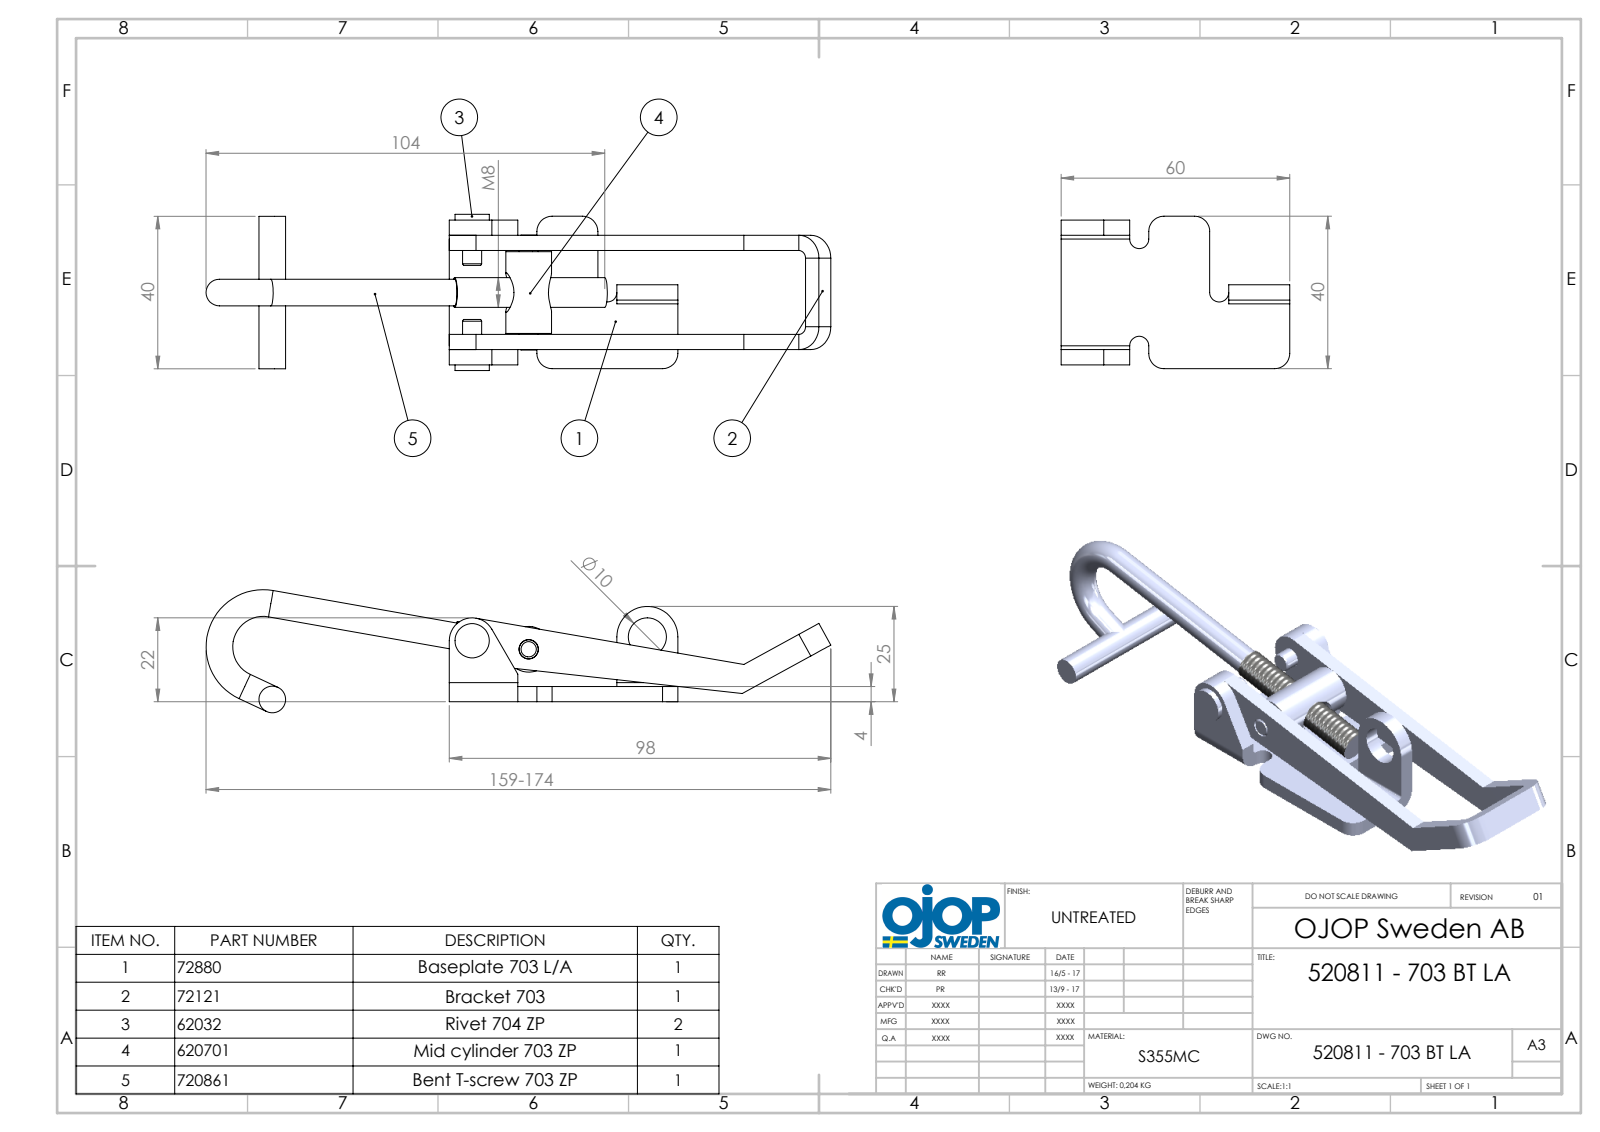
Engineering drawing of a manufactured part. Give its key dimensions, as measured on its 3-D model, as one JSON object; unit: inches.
{"part_name": "520811 - 703 BT LA; 704 - Rivet Gradin; 703- Platta LA; 703 - Rulle (+2 more)", "step_written_by": "SolidWorks 2015 (AUTOMOTIVE_DESIGN)", "units": "inches", "bodies": {"solids": 6, "faces": 146, "planar": 66, "cylindrical": 66, "other": 14}, "overall_size": [6.456, 1.614, 1.272], "volume_in3": 1.649, "surface_area_in2": 28.31, "round_holes": [[0.201, 2], [0.283, 1], [0.303, 1], [0.394, 1]], "round_bosses_or_shafts": [[0.276, 4], [0.197, 2], [0.472, 1], [0.354, 1], [0.307, 1]], "partial_cylinders_radius": [[0.157, 4], [0.039, 3], [0.098, 3], [0.197, 3], [0.236, 3], [0.079, 2], [0.315, 1]], "face_to_face_distances": [0.157, 1.024, 1.181, 0.866, 0.669, 0.512, 0.354, 0.827, 0.315, 1.339], "hole_center_spacings": [0.591, 1.233, 1.811]}
